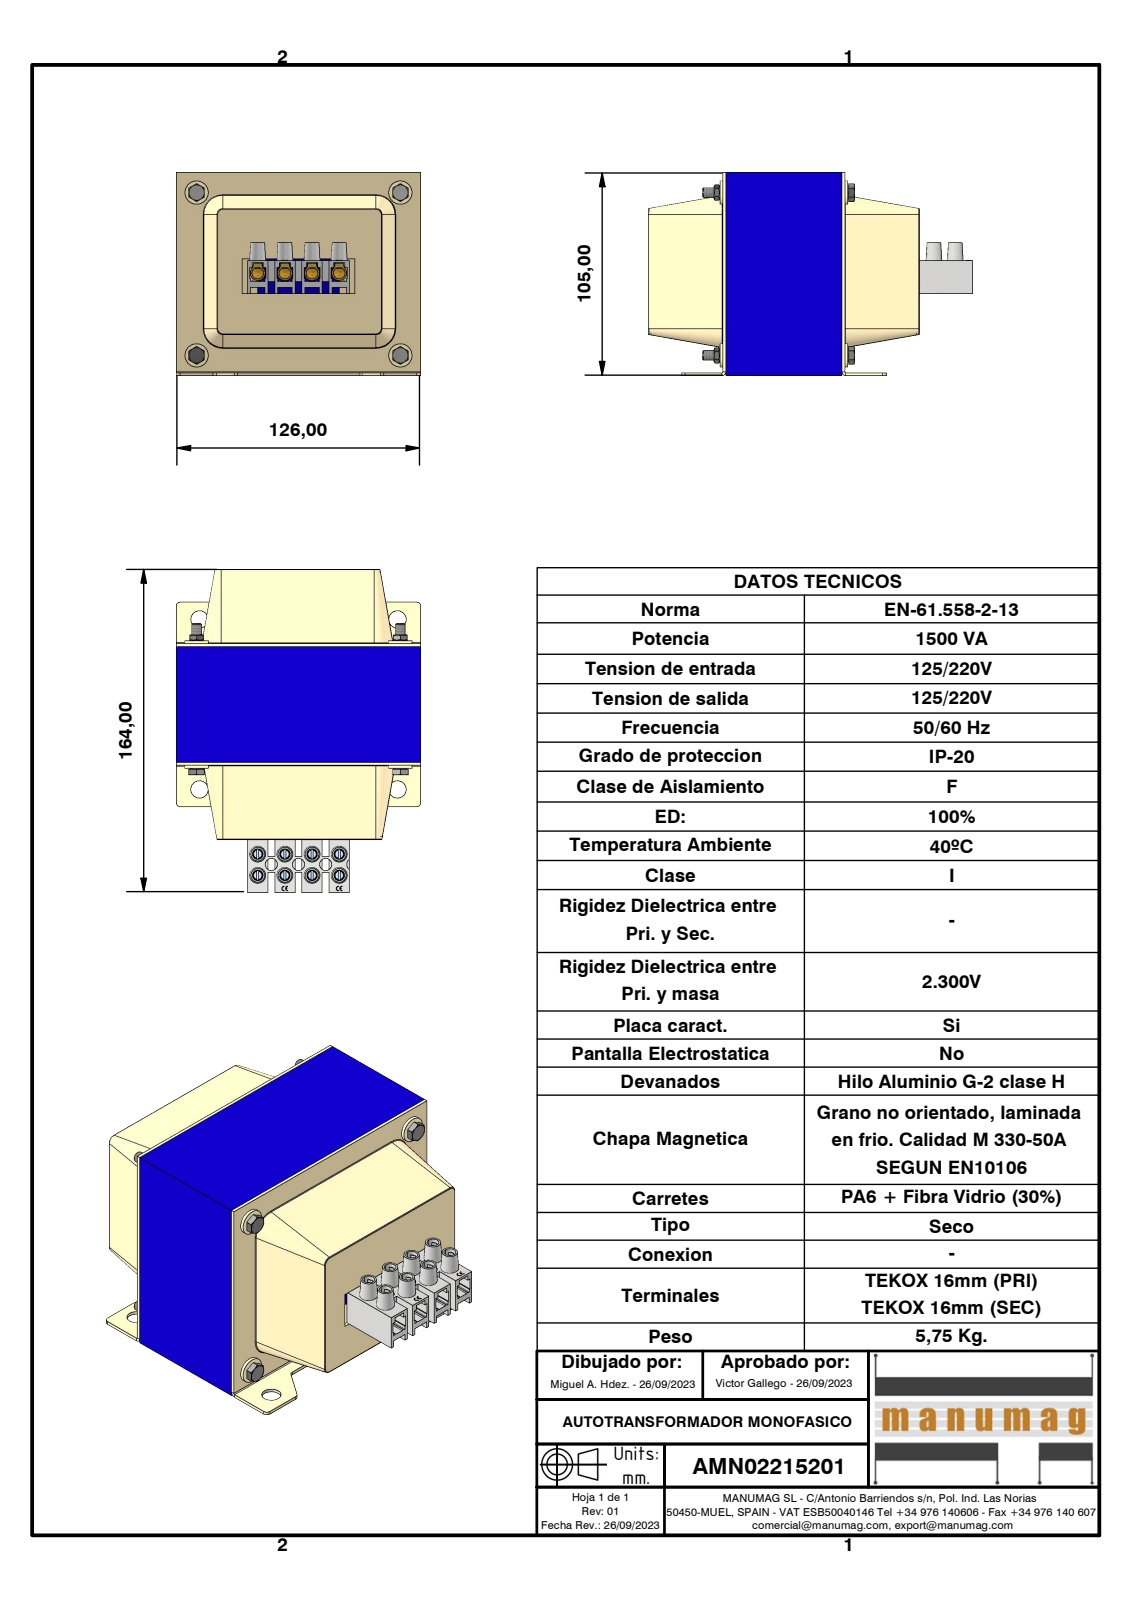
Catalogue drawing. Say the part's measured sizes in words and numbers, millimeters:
The part is named "AMN02215201; EI126 x 105 - 60 Azul; TAPA RC42 CIEGA; TAPA RC42 VENTANA 4 ELEMENTOS 16 (+8 more)". Its 3-D file was written by "Autodesk Inventor 2023 (AUTOMOTIVE_DESIGN)". It is 40 solids with 1657 faces: 1104 planar, 226 cylindrical and 327 other. Overall it measures 167.5 by 126 by 105 millimeters. Its volume is 690 288 cubic millimeters and its surface area 203 095 square millimeters. Round holes: 12 of diameter 3.24, 8 of diameter 5.5, 8 of diameter 6, 4 of diameter 5, 4 of diameter 6.5, 4 of diameter 9, 3 of diameter 6.3. Round bosses or shafts: 8 of diameter 4, 4 of diameter 12, 4 of diameter 6.7, 4 of diameter 5.9, 4 of diameter 4.57. Partial cylindrical surfaces (rounded edges, fillets, slot ends): 16 of radius 0.38, 16 of radius 2.75, 14 of radius 2, 8 of radius 0.82, 8 of radius 3, 6 of radius 0.22, 4 of radius 0.1, 4 of radius 0.81. The main face-to-face distances are 1.5, 38.5, 21, 100, 63, 84, 60, 105, 42, 37. The hole center spacings are 14, 28, 8.81, 9, 17.8, 11, 21.67, 21.75.
